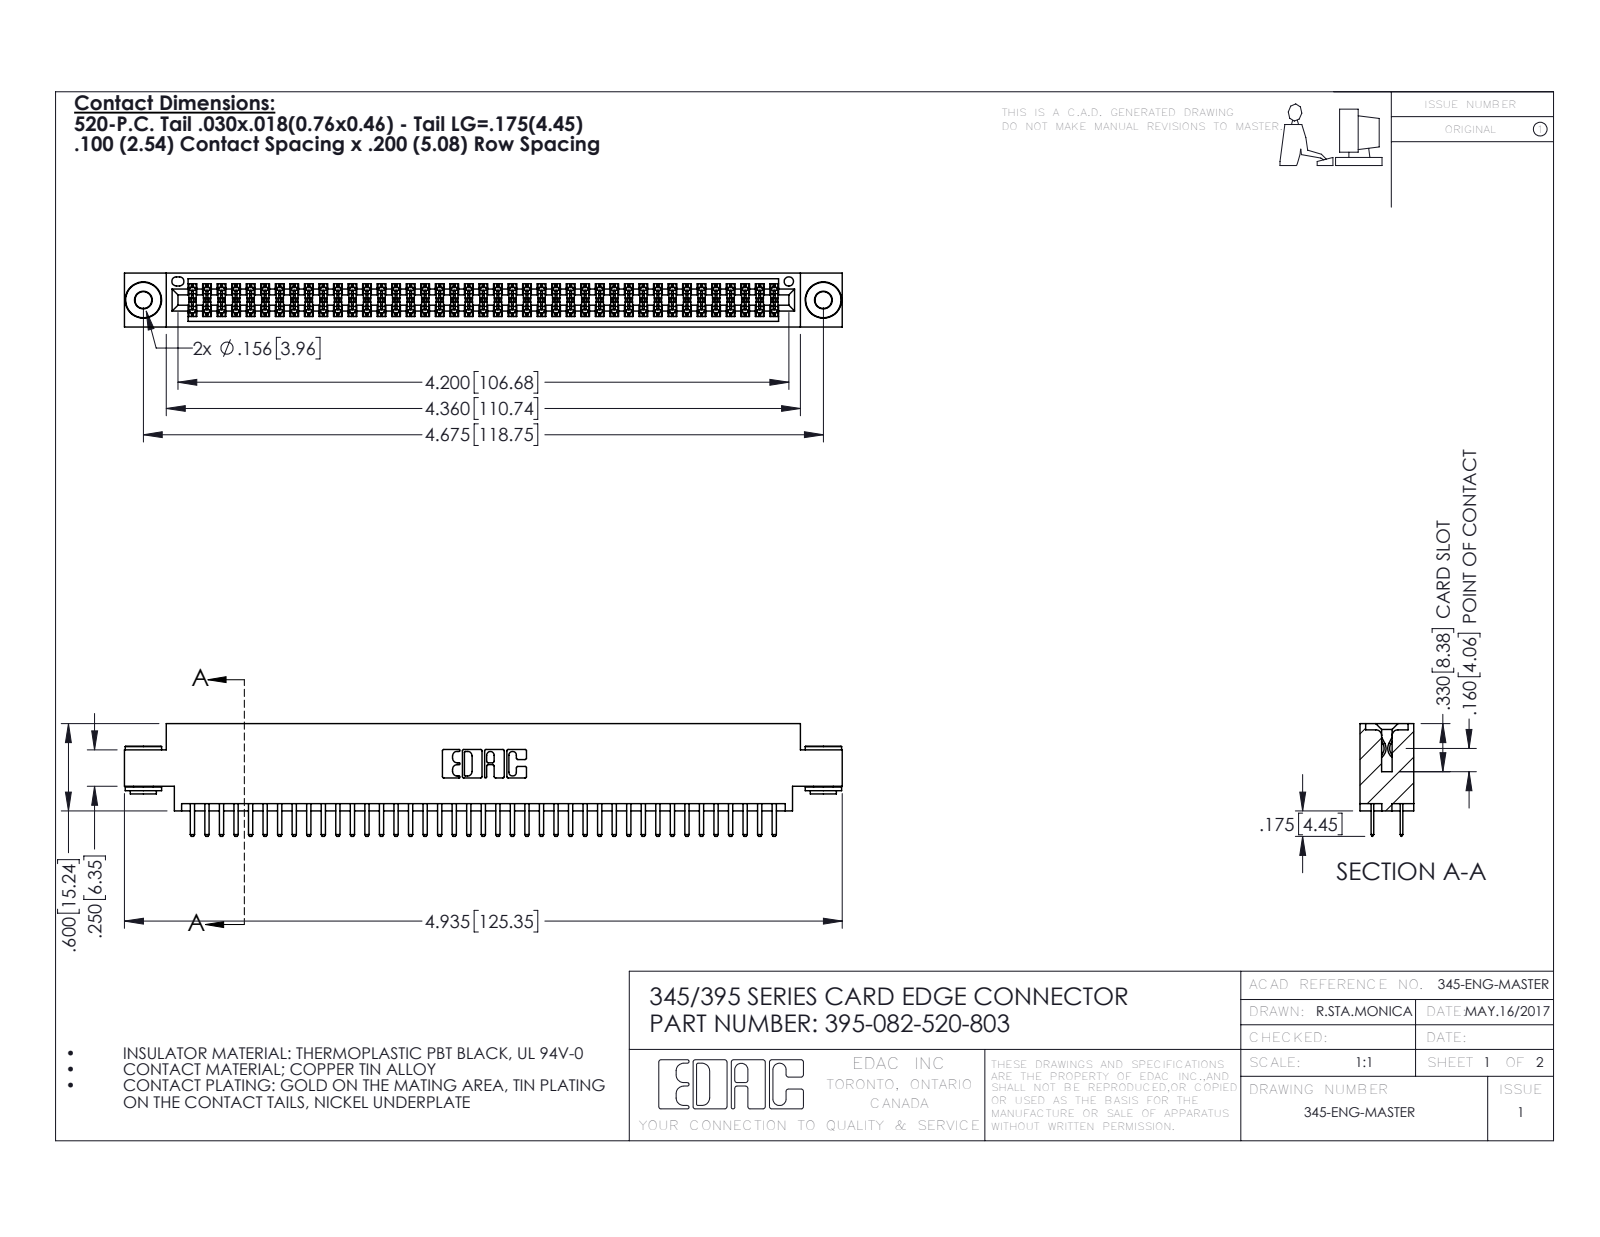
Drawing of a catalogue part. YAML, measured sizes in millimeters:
part_name: "345-250-002_345-250-002-102; 395-082-520-803; 345 Part_0.170 Offset - 0.156 Dia-TH; 345-292-001_345-293-120"
step_written_by: "SolidWorks 2016 (CONFIG_CONTROL_DESIGN)"
units: millimeters
bodies: {solids: 85, faces: 4596, planar: 2964, cylindrical: 1624, other: 8}
overall_size: [125.3, 19.7, 9.4]
volume: 12000
surface_area: 18050
round_holes:
  - {diameter: 2.9, count: 2}
  - {diameter: 4, count: 2}
  - {diameter: 1.6, count: 1}
round_bosses_or_shafts:
  - {diameter: 6.4, count: 2}
  - {diameter: 4.6, count: 2}
  - {diameter: 3.5, count: 2}
partial_cylinders:
  - {radius: 0.2, count: 123}
  - {radius: 0.3, count: 86}
  - {radius: 0.3, count: 22}
  - {radius: 0.2, count: 6}
  - {radius: 0.8, count: 6}
  - {radius: 0.7, count: 3}
  - {radius: 0.4, count: 2}
  - {radius: 0.5, count: 2}
face_to_face_distances: [1.8, 7.6, 5.1, 9.4, 2.5, 6.9, 0.6, 5.7, 4.4, 0.6]
hole_center_spacings: [6.9, 112.8, 118.7]
